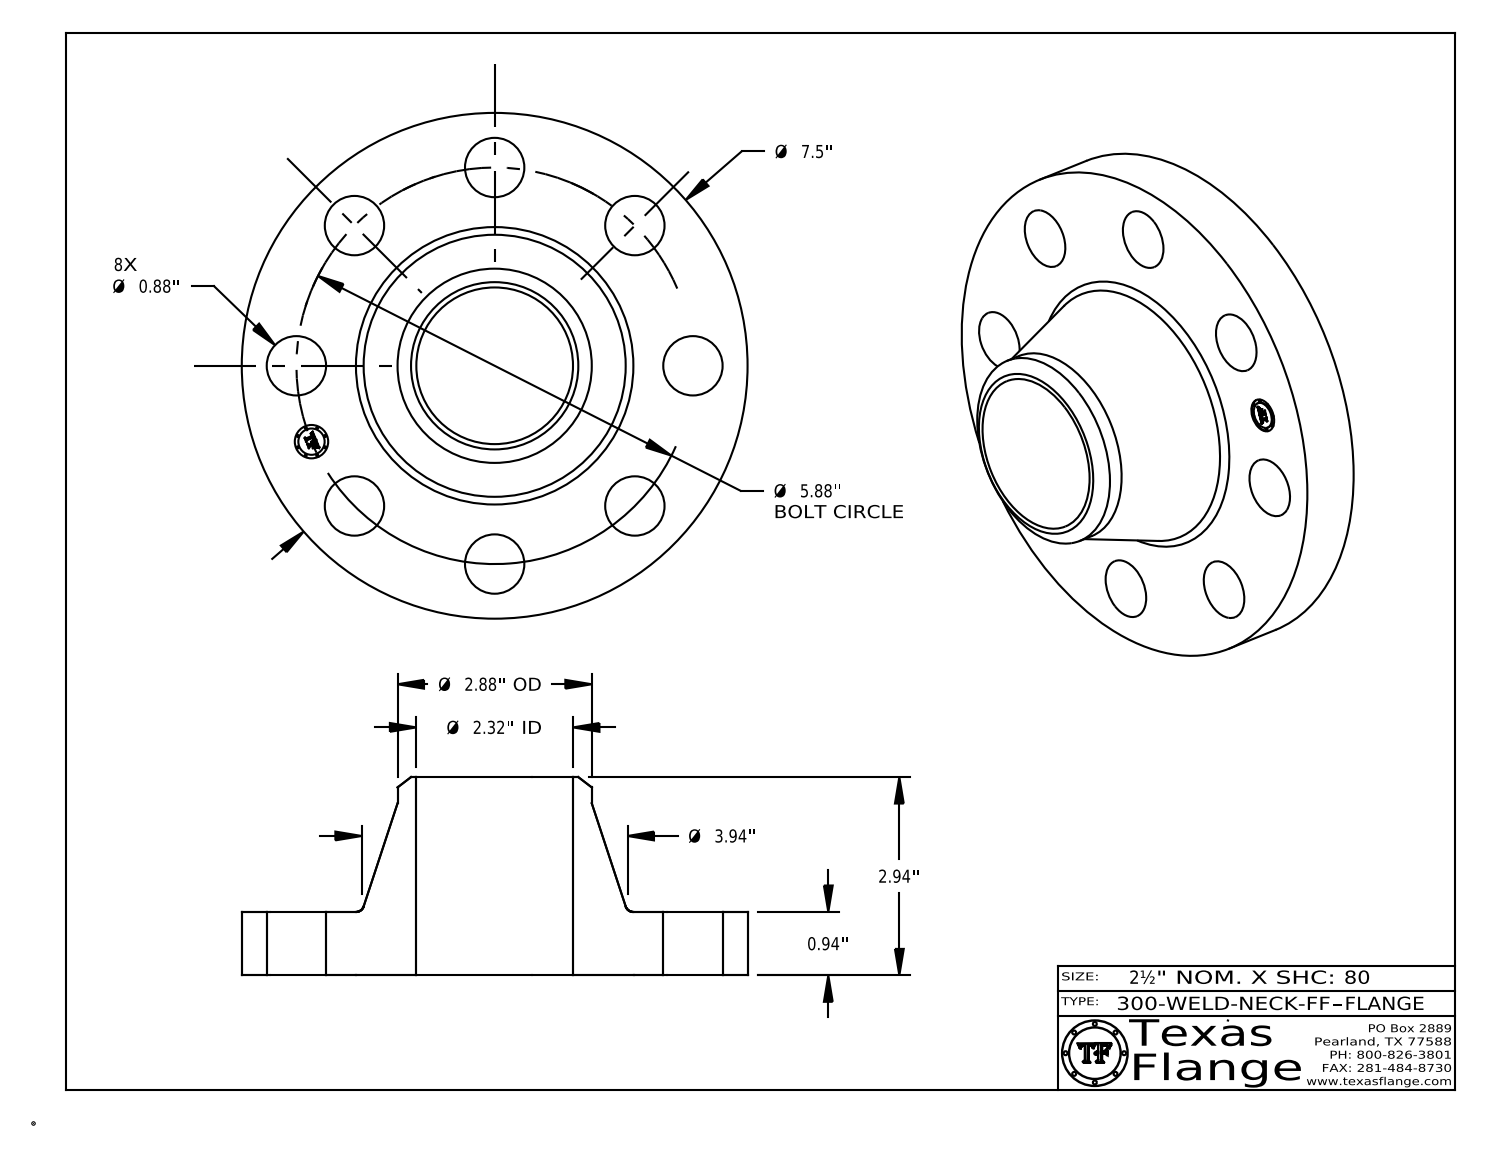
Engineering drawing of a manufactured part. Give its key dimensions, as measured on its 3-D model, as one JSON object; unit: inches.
{"part_name": "300-WELD-NECK-FF", "step_written_by": "CATIA V5 STEP AP214 (AUTOMOTIVE_DESIGN)", "units": "inches", "bodies": {"solids": 1, "faces": 417, "planar": 369, "cylindrical": 42, "other": 6}, "overall_size": [7.5, 7.5, 2.94], "volume_in3": 41.74, "surface_area_in2": 149.4, "round_holes": [[0.88, 8], [0.495, 1], [2.323, 1]], "round_bosses_or_shafts": [[0.03, 8], [7.5, 1], [2.88, 1], [0.39, 1]], "face_to_face_distances": [0.94, 2.94, 2, 0.015, 0.925, 2.015, 0.148, 0.145, 0.027, 0.096], "hole_center_spacings": [2.25, 5.432, 2.94, 2.94, 4.157, 4.158, 3.267, 5.88]}
